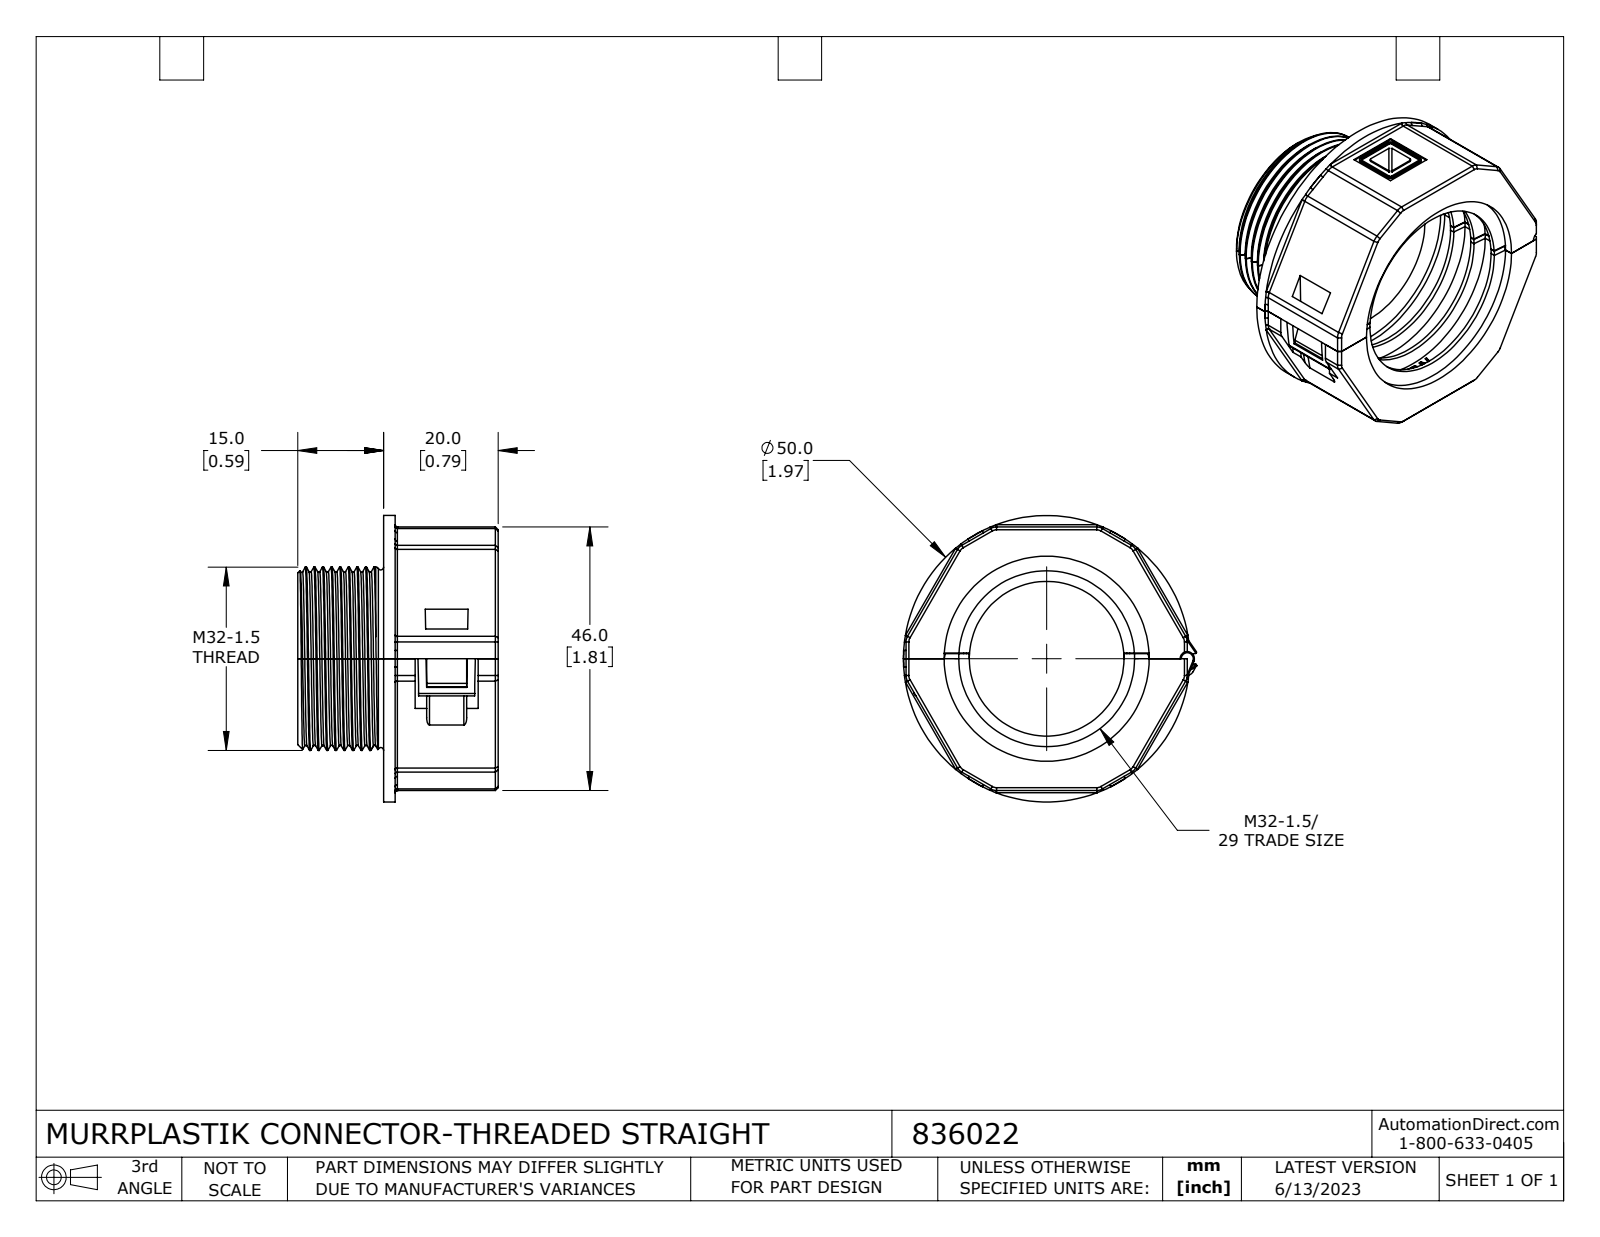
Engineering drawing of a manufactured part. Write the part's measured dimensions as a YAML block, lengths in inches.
part_name: "836022"
step_written_by: "SolidWorks 2021 (CONFIG_CONTROL_DESIGN)"
units: inches
bodies: {solids: 2, faces: 753, planar: 351, cylindrical: 156, other: 246}
overall_size: [2.015, 1.969, 1.378]
volume: 1.259
surface_area: 22.19
round_holes:
  - {diameter: 0.098, count: 1}
  - {diameter: 0.197, count: 1}
  - {diameter: 1.063, count: 1}
  - {diameter: 1.209, count: 1}
  - {diameter: 1.409, count: 1}
round_bosses_or_shafts:
  - {diameter: 1.969, count: 1}
  - {diameter: 1.26, count: 1}
partial_cylinders:
  - {radius: 0.016, count: 16}
  - {radius: 0.079, count: 15}
  - {radius: 0.008, count: 13}
  - {radius: 0.02, count: 11}
  - {radius: 0.013, count: 4}
  - {radius: 0.025, count: 4}
  - {radius: 0.039, count: 2}
  - {radius: 0.059, count: 2}
face_to_face_distances: [1.811, 0.787, 0.906, 0.669, 0.118, 0.039, 0.709, 1.934, 0.079, 1.378]
hole_center_spacings: [0.967]
